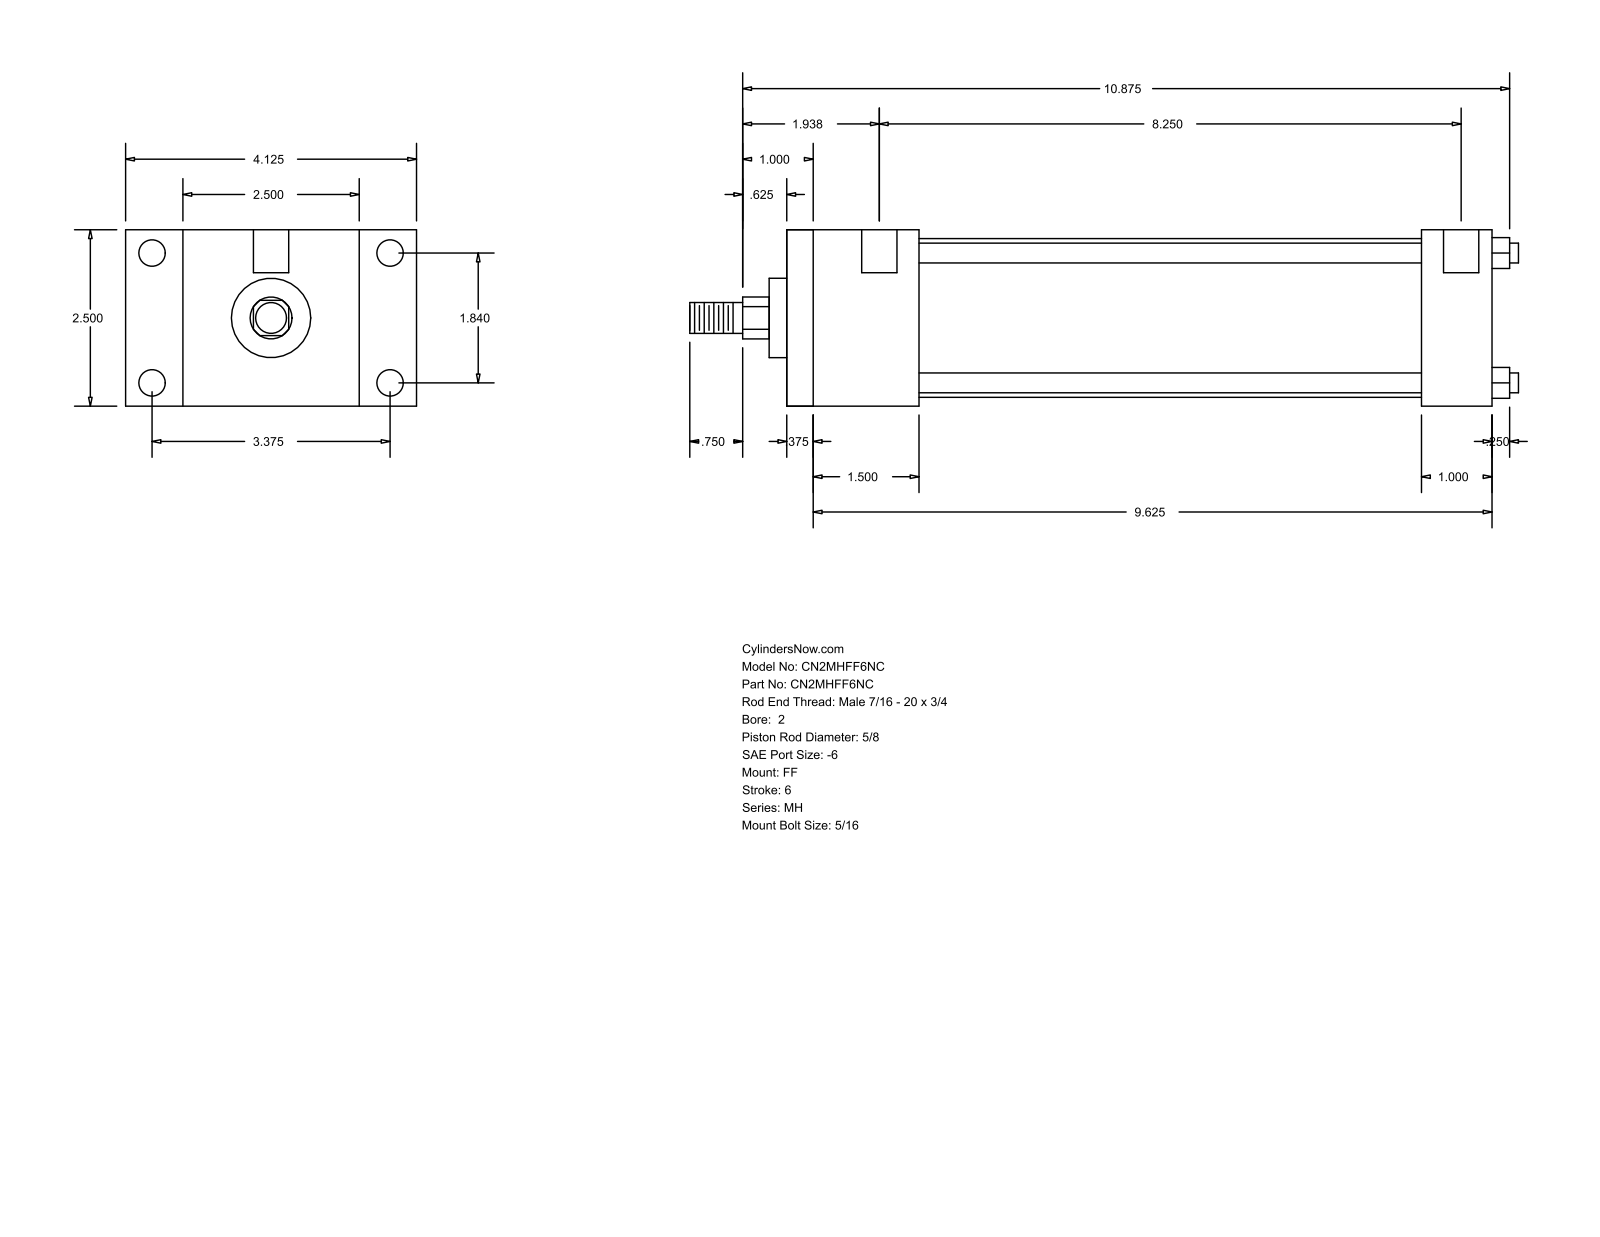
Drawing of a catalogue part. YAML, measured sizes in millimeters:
part_name: "MH_FF__0200_0.625"
step_written_by: "GSSL Pune (CONFIG_CONTROL_DESIGN)"
units: millimeters
bodies: {solids: 0, faces: 92, planar: 64, cylindrical: 28, other: 0}
overall_size: [298.45, 104.78, 63.5]
round_holes:
  - {diameter: 5.56, count: 4}
  - {diameter: 9.53, count: 4}
  - {diameter: 12.7, count: 2}
round_bosses_or_shafts:
  - {diameter: 7.14, count: 4}
  - {diameter: 57.15, count: 1}
  - {diameter: 28.57, count: 1}
  - {diameter: 15.88, count: 1}
  - {diameter: 11.11, count: 1}
partial_cylinders:
  - {radius: 7.54, count: 1}
face_to_face_distances: [63.5, 254, 9.52, 244.48, 38.1, 47.62, 228.59, 219.07, 180.97, 206.38]
hole_center_spacings: [46.74, 85.72, 97.63, 217.49, 3.18, 4.76, 209.55, 212.73]
